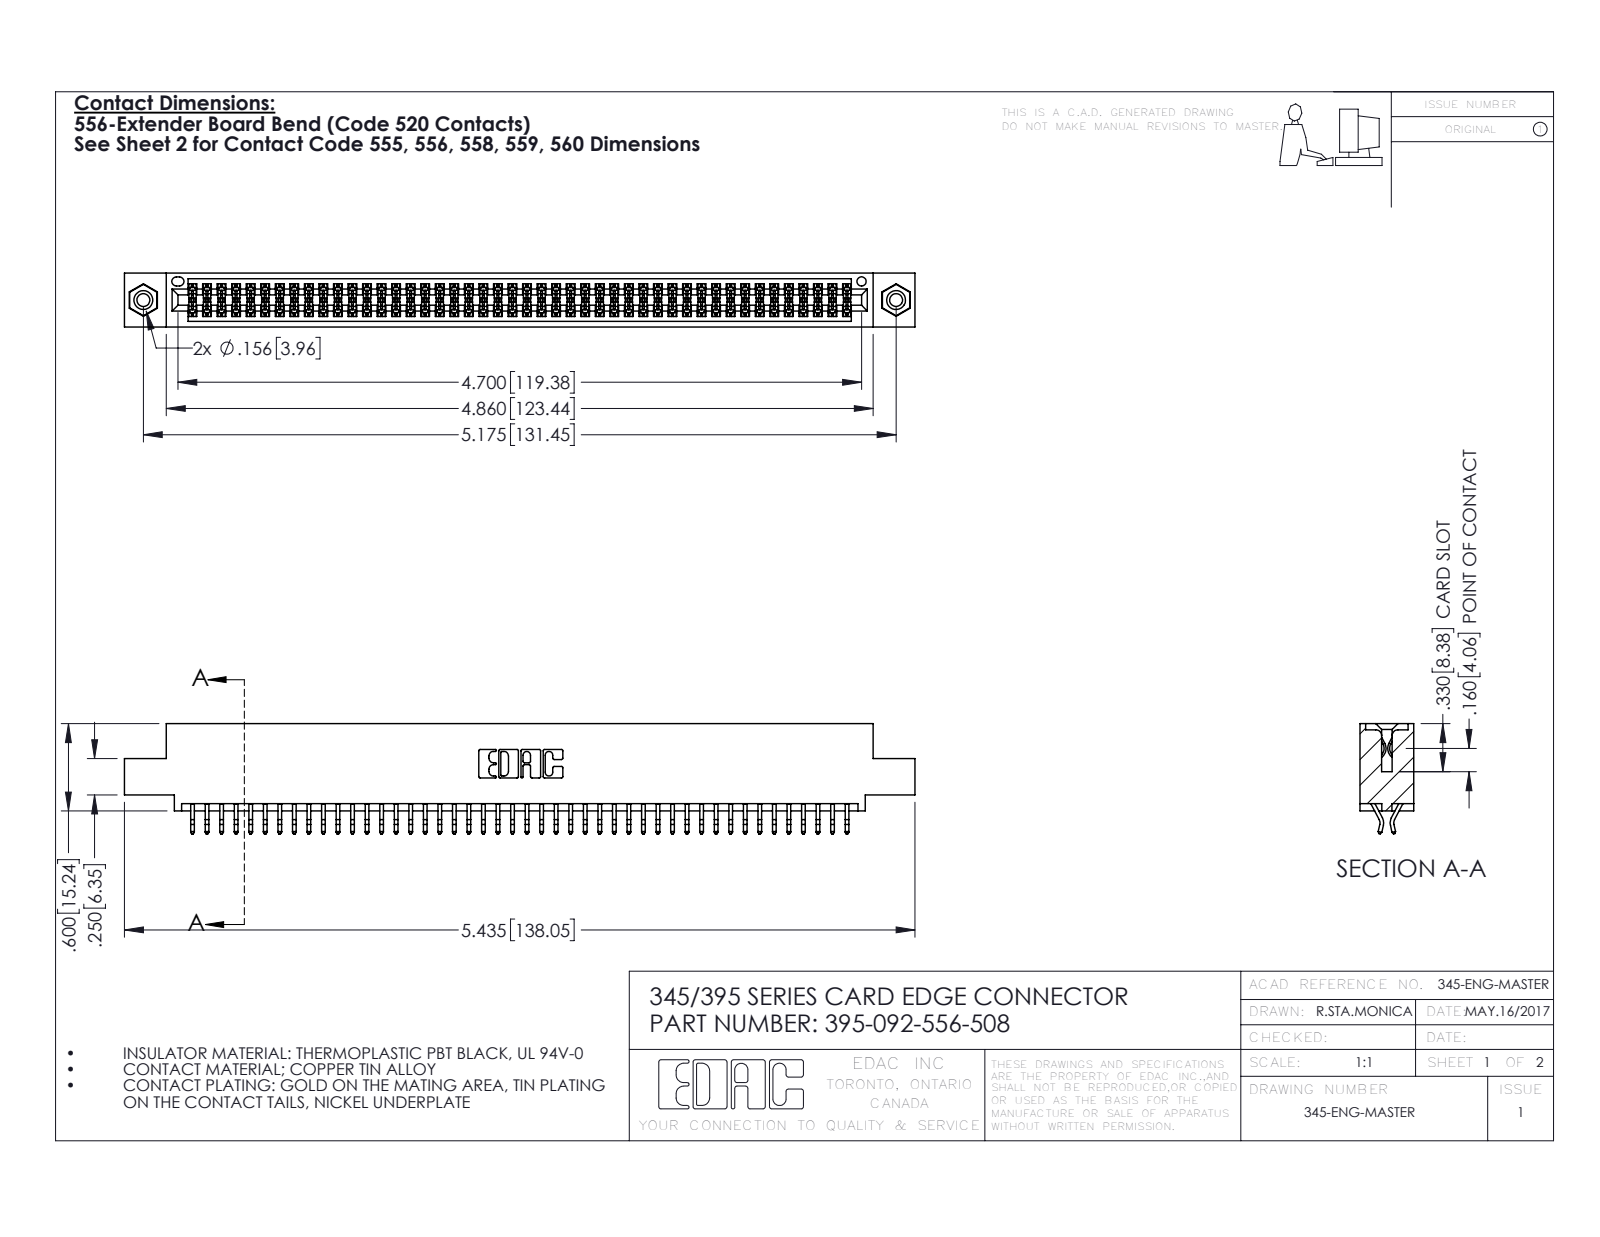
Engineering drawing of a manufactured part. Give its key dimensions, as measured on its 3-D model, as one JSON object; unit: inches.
{"part_name": "395-092-556-508; 345-250-001_345-250-003-102; 345 Part_0.110 Offset - 0.156 Dia-TI; 345-292-001_556 Tail", "step_written_by": "SolidWorks 2016 (CONFIG_CONTROL_DESIGN)", "units": "inches", "bodies": {"solids": 95, "faces": 5342, "planar": 3520, "cylindrical": 1806, "other": 16}, "overall_size": [5.435, 0.757, 0.37], "volume_in3": 0.816, "surface_area_in2": 30.78, "round_holes": [[0.089, 2], [0.125, 2], [0.156, 2], [0.064, 1]], "round_bosses_or_shafts": [[0.155, 2]], "partial_cylinders_radius": [[0.006, 138], [0.01, 22], [0.007, 6], [0.031, 6], [0.026, 3], [0.01, 2], [0.014, 2], [0.019, 2]], "face_to_face_distances": [0.072, 0.298, 0.37, 0.2, 0.025, 0.098, 0.272, 0.225, 0.175, 0.149], "hole_center_spacings": [0.27, 4.939, 5.175]}
